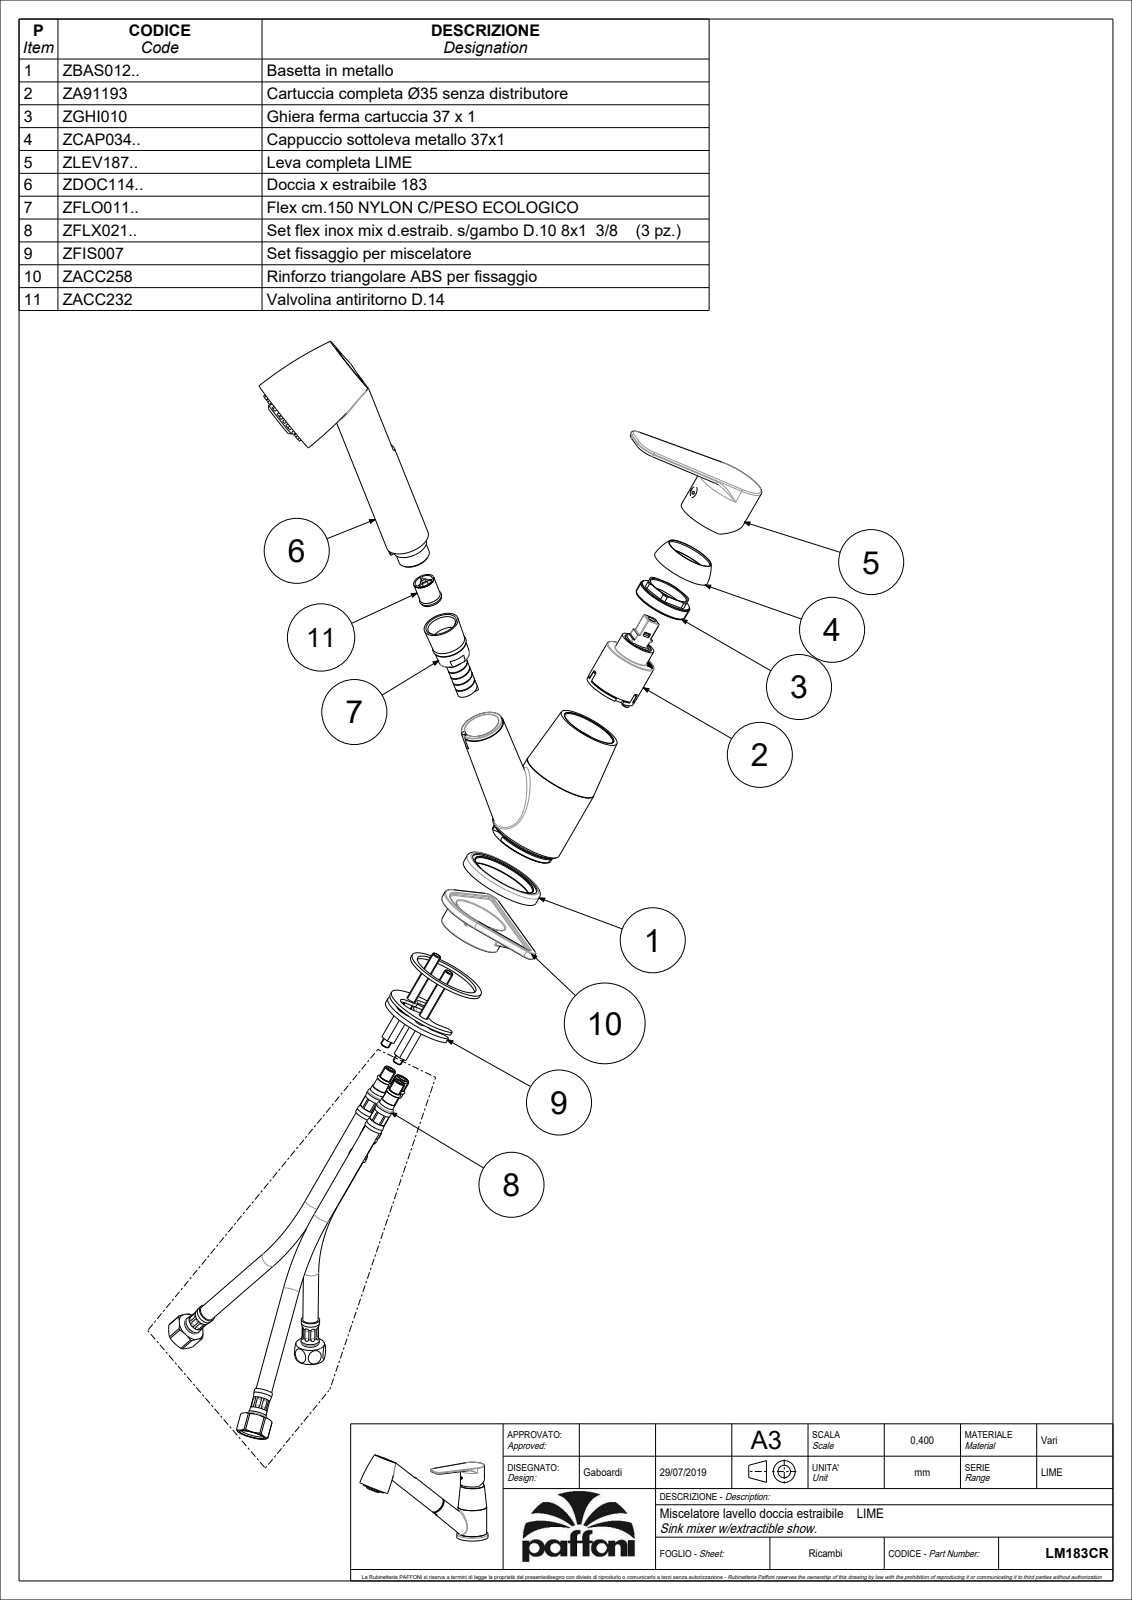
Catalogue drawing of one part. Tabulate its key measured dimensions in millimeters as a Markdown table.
| quantity | value |
| --- | --- |
| part name | LM183CR |
| STEP written by | CREO PARAMETRIC BY PTC INC, 2020044 (CONFIG_CONTROL_DESIGN) |
| units | millimeters |
| bodies | 2 solids, 1141 faces (467 planar, 426 cylindrical, 248 other) |
| overall size | 250.31 × 173.53 × 54.7 |
| volume | 339 821 mm³ |
| surface area | 119 734 mm² |
| round holes (diameter × count) | 0.5 × 32, 7 × 5, 4 × 3, 12 × 3, 8 × 2, 8.6 × 2, 3 × 1, 3.3 × 1, 3.4 × 1, 4.6 × 1, 5.5 × 1, 6 × 1 |
| round bosses / shafts (diameter × count) | 2 × 32, 42 × 2, 9 × 2, 8 × 2, 6.8 × 2, 6 × 2, 54.7 × 1, 50 × 1 |
| partial cylindrical surfaces (radius × count) | 0.5 × 39, 0.3 × 19, 1 × 18, 2 × 4, 4.5 × 3, 1.2 × 2, 10 × 2, 12.5 × 2 |
| main face-to-face distances | 3.5, 2.5, 1, 126.7, 130.2, 127.7, 83.3, 30.5, 73.3, 33 |
| hole center spacings | 15, 29.43, 4.04, 10.4, 13.74, 29.31, 32.75, 4.72 |
